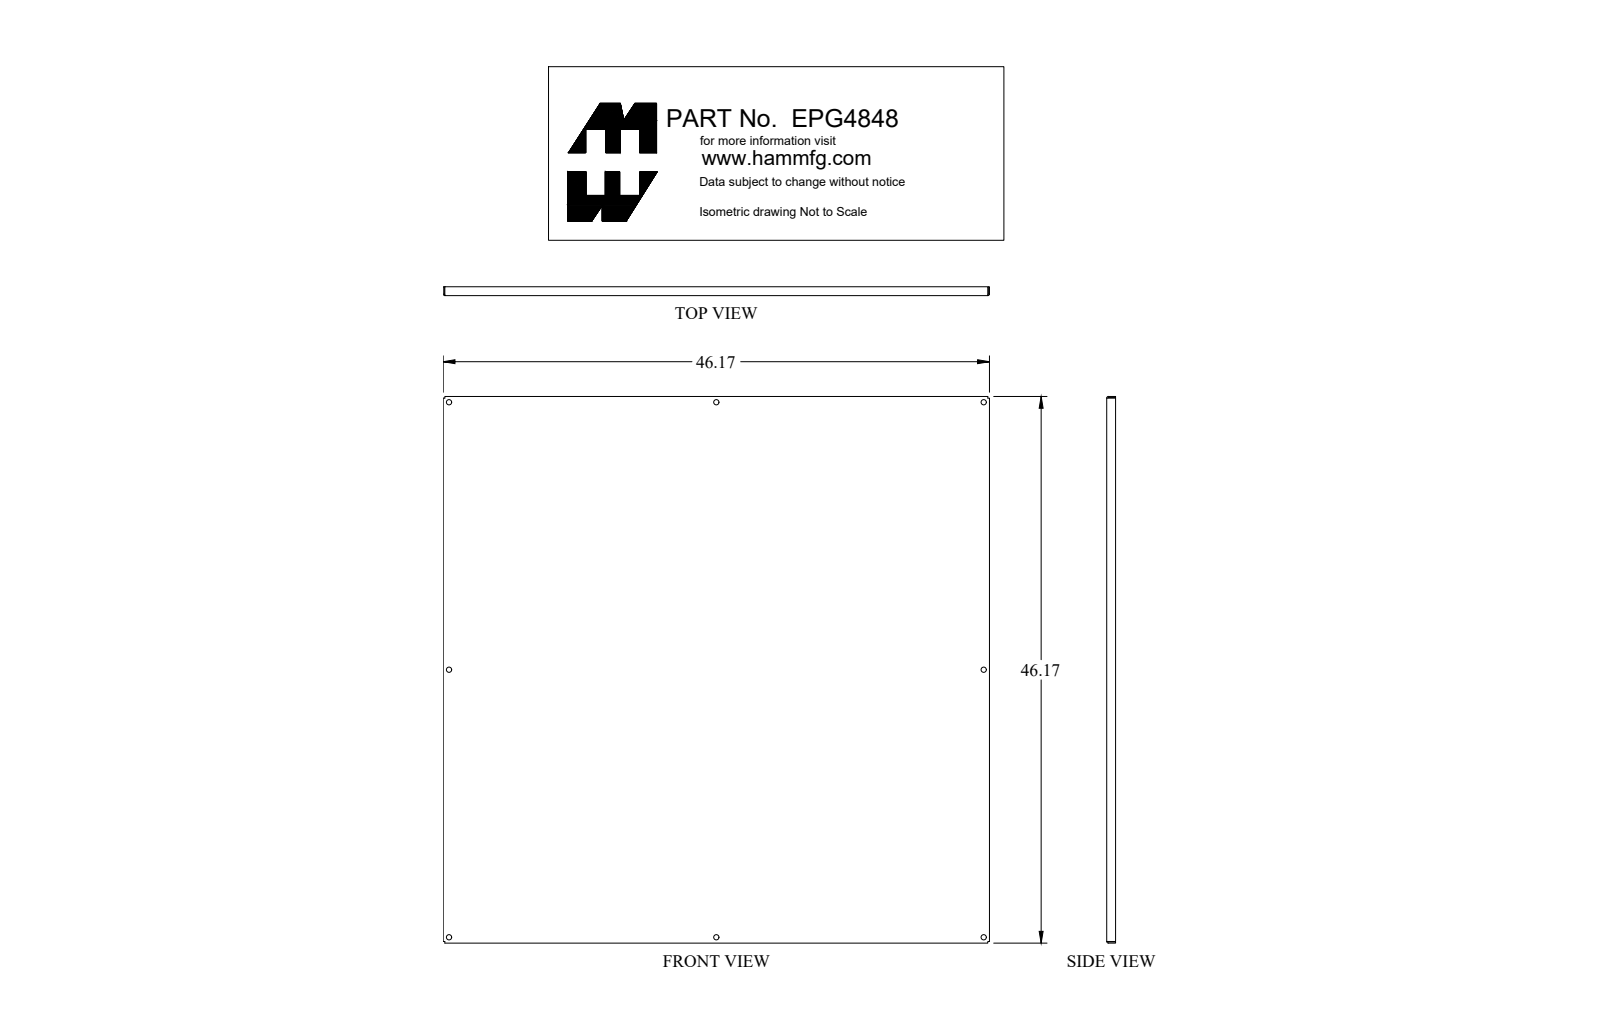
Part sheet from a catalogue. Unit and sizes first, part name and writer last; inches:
Units: inches
Overall size (bounding box): 46.17 × 46.17 × 0.75
Round holes (diameter × count): ⌀0.437 ×8
Partial cylindrical surfaces — rounded edges, fillets, slot ends (radius × count): R0.048 ×4, R0.143 ×4
Main face-to-face distances: 0.095, 46.075, 46.17, 45.98, 0.75, 0.655, 0.143, 46.027, 0.048, 45.932
Hole centre spacings: 22.594, 50.522, 45.188, 31.953, 63.906
Volume: 213.1 in³ · Surface area: 4 505 in²
Bodies: 1 solid, 46 faces (22 planar, 24 cylindrical, 0 other)
Part name (STEP PRODUCT): EPG4848
STEP written by: SolidWorks 2018 (AUTOMOTIVE_DESIGN)
